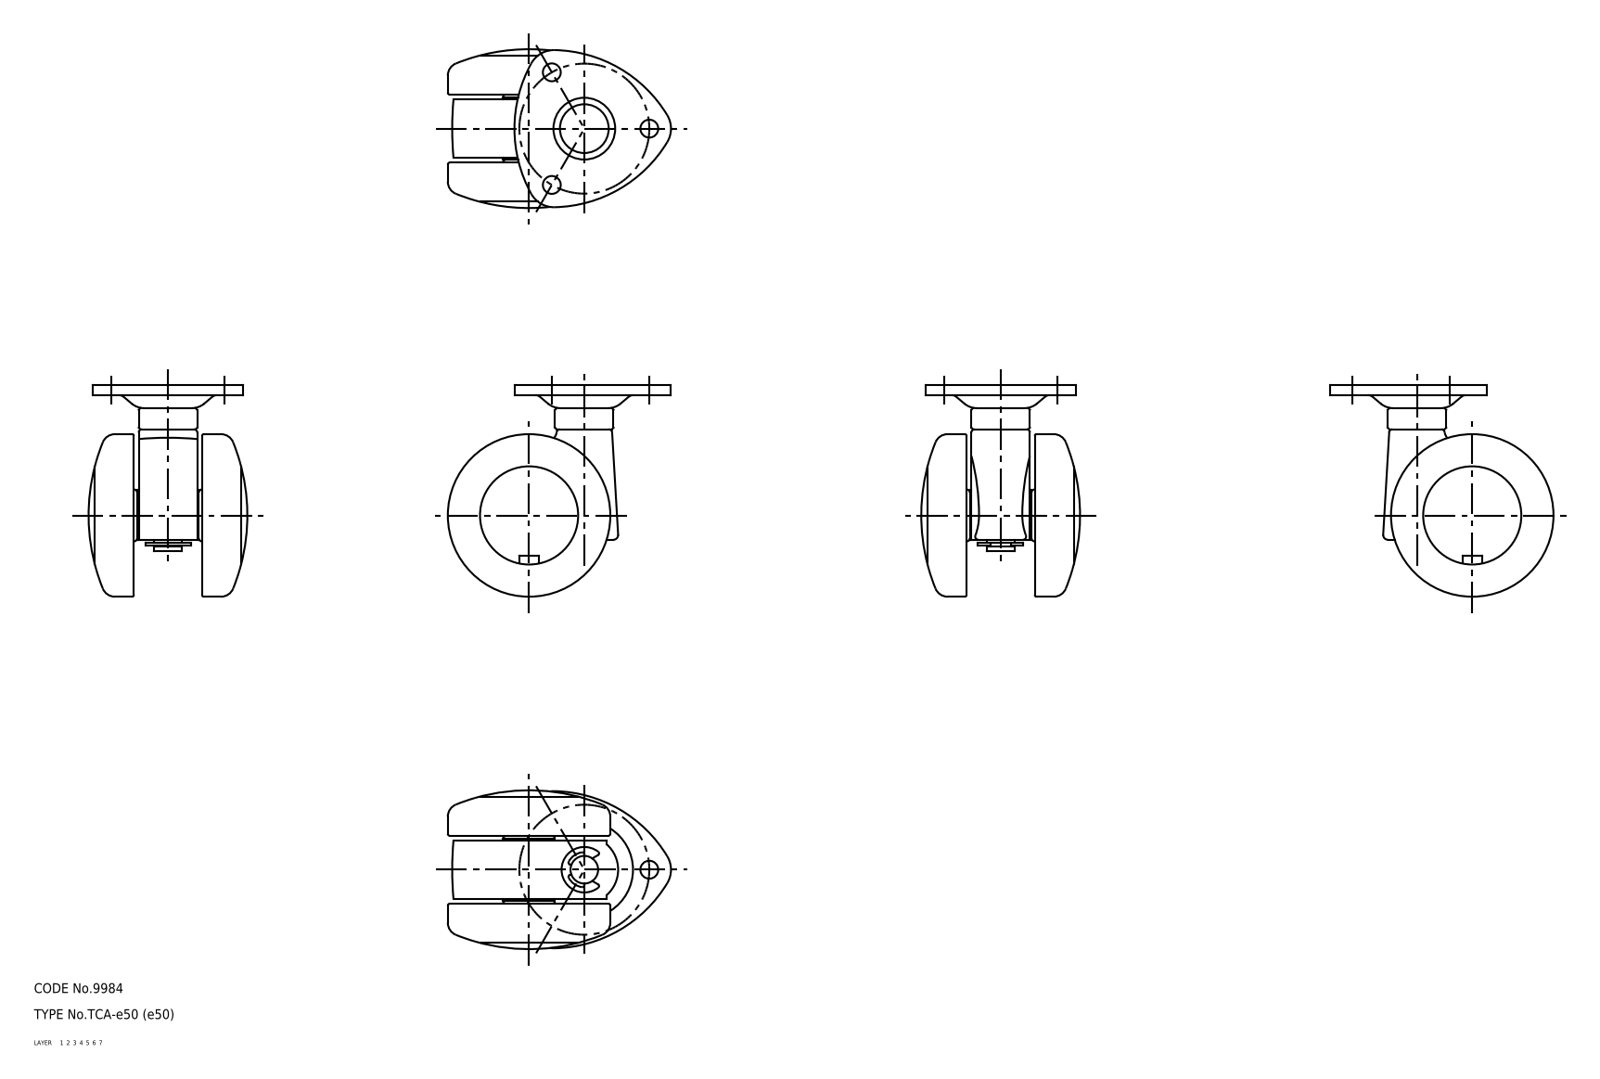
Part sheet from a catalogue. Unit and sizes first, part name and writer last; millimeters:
Units: millimetres
Overall size (bounding box): 68.67 × 65 × 48.86
Volume: 66 838 mm³ · Surface area: 29 474 mm²
Bodies: 5 solids, 148 faces (0 planar, 0 cylindrical, 148 other)
Part name (STEP PRODUCT): wheel_mr; wheel; mounting plate; main shaft (+1 more)
STEP written by: CADfix (AUTOMOTIVE_DESIGN)
